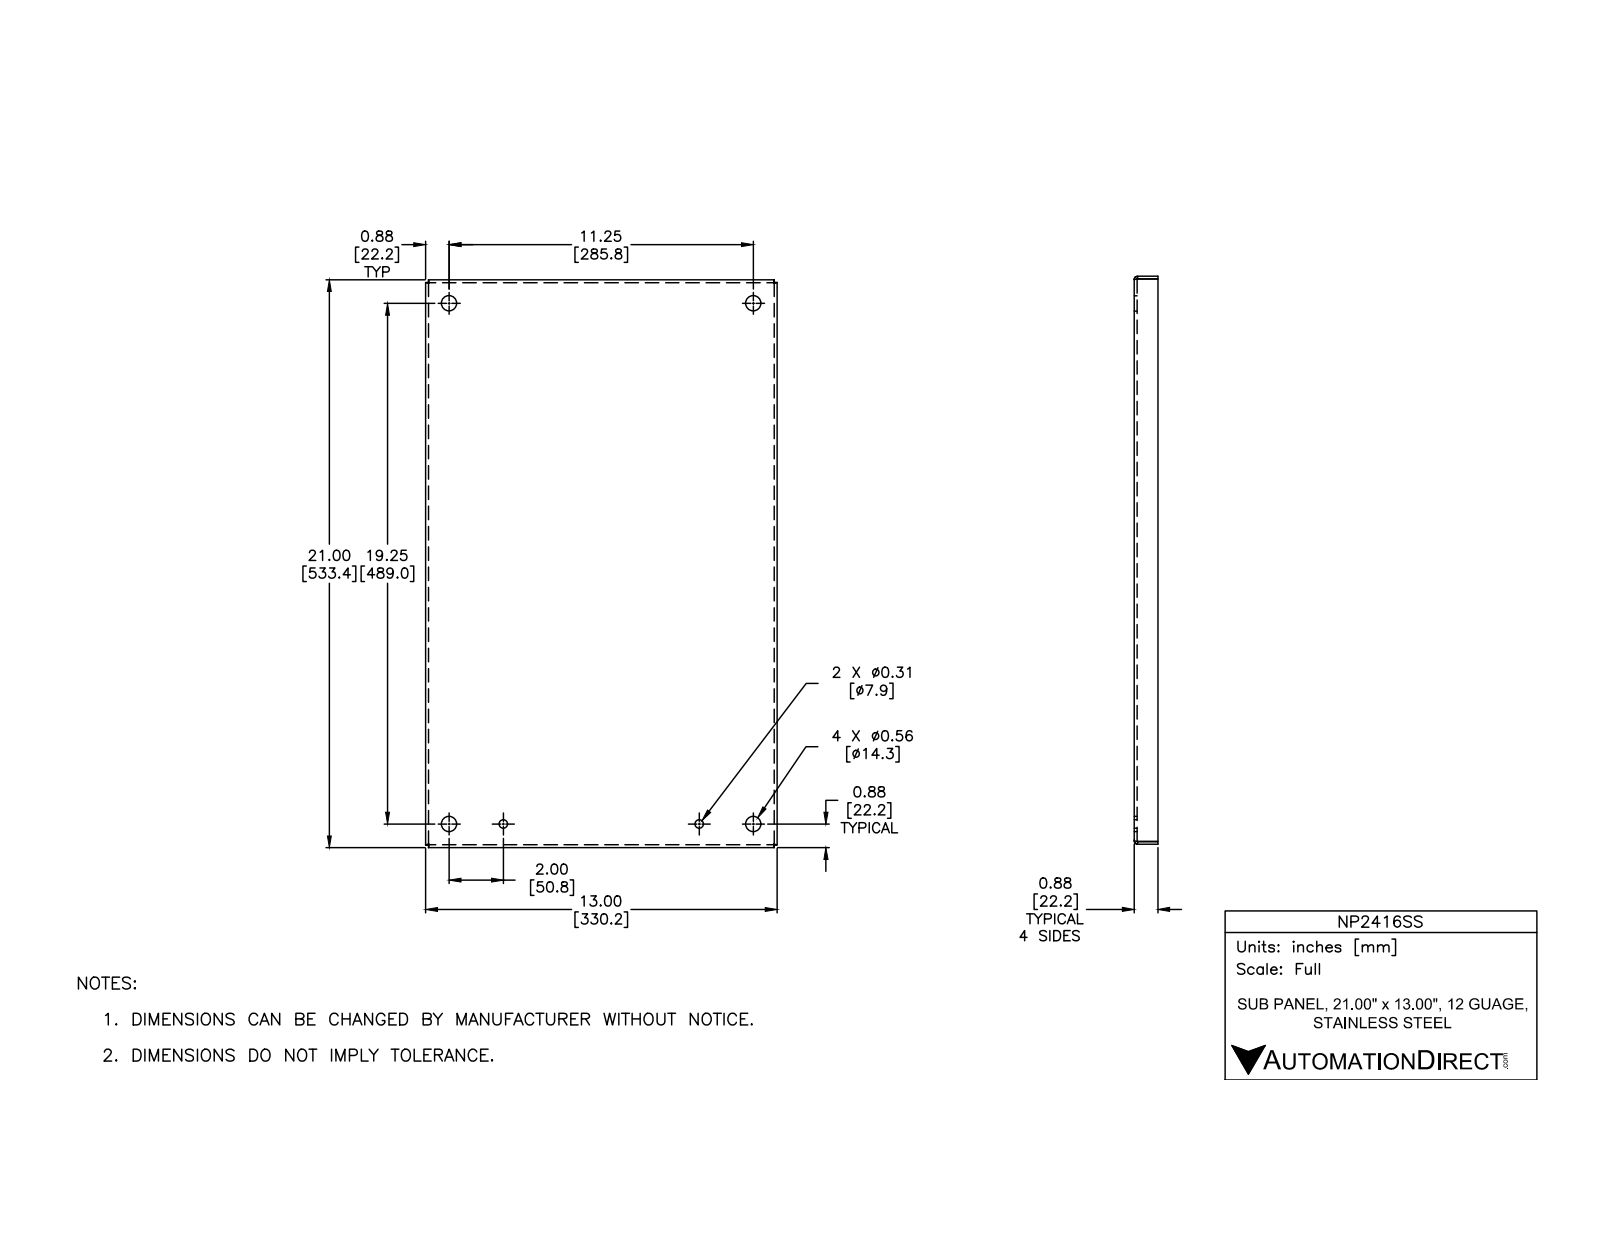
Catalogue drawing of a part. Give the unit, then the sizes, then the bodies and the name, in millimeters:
Units: millimetres
Overall size (bounding box): 533.4 × 330.2 × 22.2
Round holes (diameter × count): ⌀14.3 ×4, ⌀7.9 ×2
Partial cylindrical surfaces — rounded edges, fillets, slot ends (radius × count): R0.8 ×4, R3.2 ×4
Main face-to-face distances: 2.4, 327.8, 531, 330.2, 325.5, 533.4, 528.7, 19.8, 22.2, 2.7
Hole centre spacings: 285.8, 489, 491.6, 542.5, 566.3, 50.8, 50.8, 184.2
Volume: 494 400 mm³ · Surface area: 420 500 mm²
Bodies: 1 solid, 44 faces (22 planar, 14 cylindrical, 8 other)
Part name (STEP PRODUCT): NP2416SS
STEP written by: Autodesk Inventor 2012 (AUTOMOTIVE_DESIGN)
